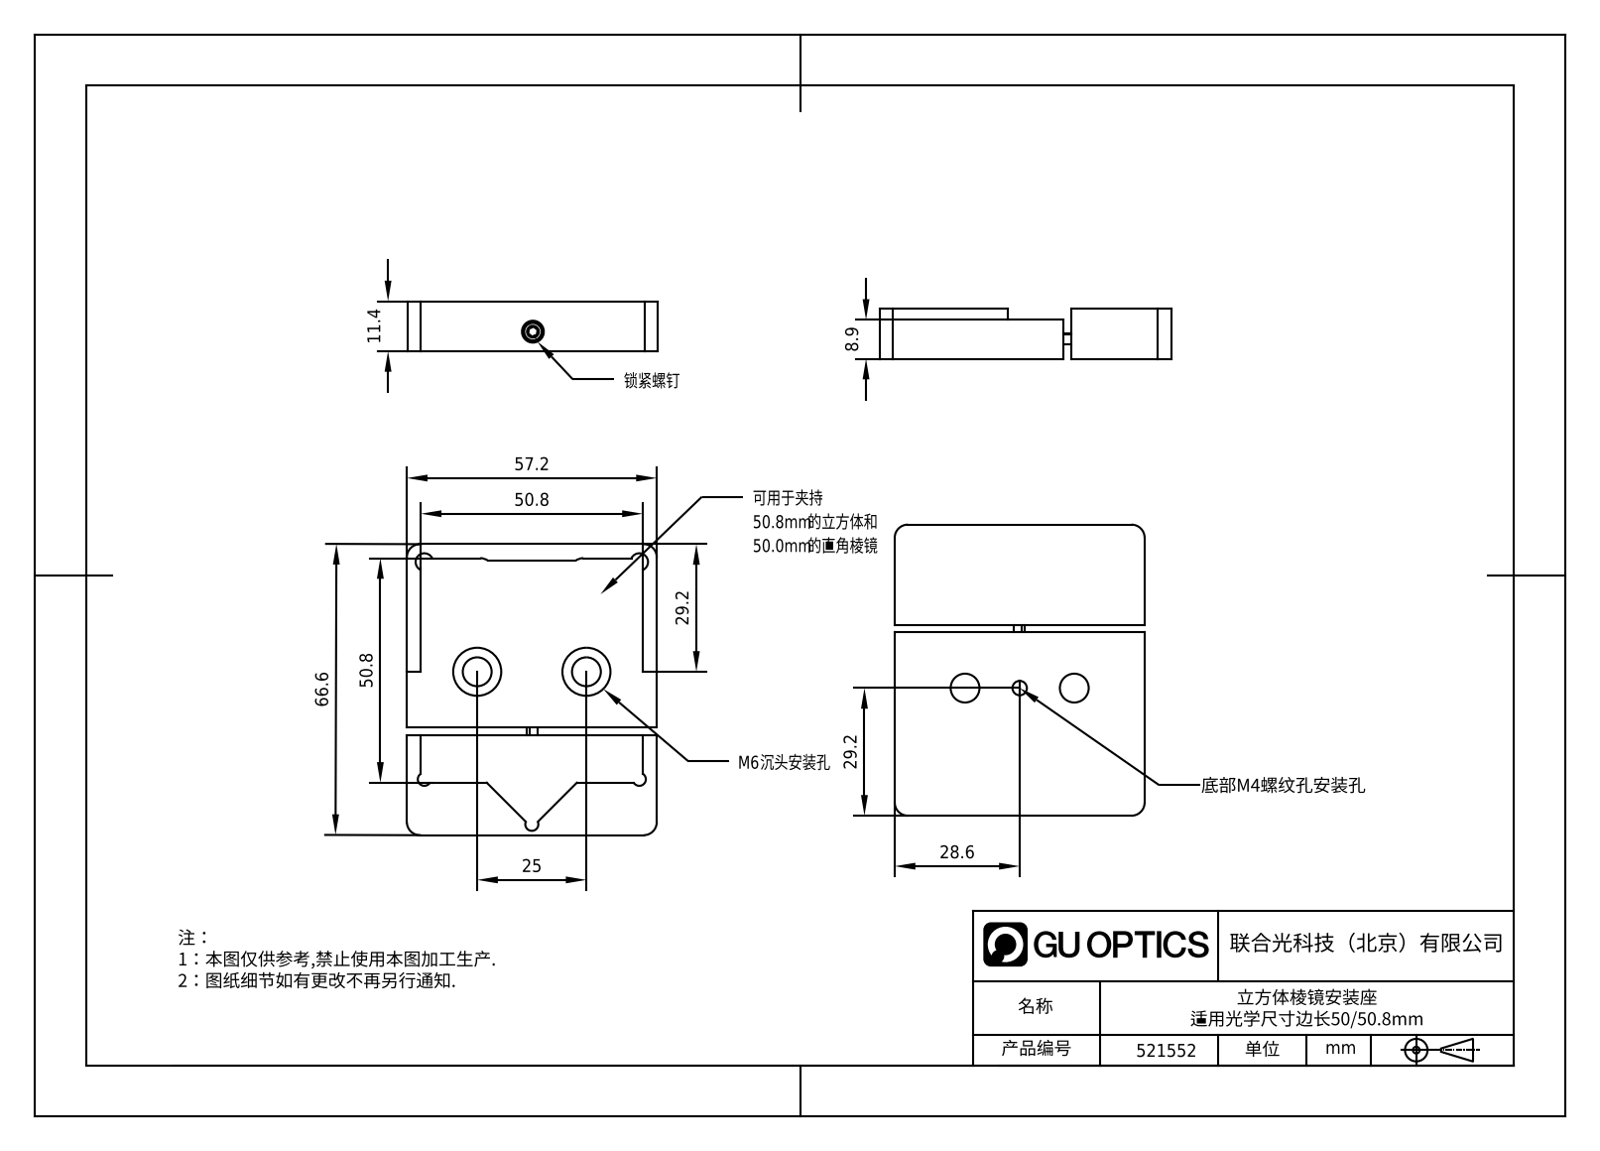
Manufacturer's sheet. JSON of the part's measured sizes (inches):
{"part_name": "1.3.13.3_ZZP-2.0_平台安装座，用于2英寸分束立方和直角棱镜，M4螺孔; 1.3.13.3.1_平台安装座主体1，用于2英寸分束立方和直角棱镜，M4螺孔; 1.3.13.3.2_平台安装座主体2，用于2英寸分束立方和直角棱镜，M4螺孔; 30.1.圆柱头内六角不锈钢螺丝_30.1.52-M2.5*25", "step_written_by": "SolidWorks 2021 (CONFIG_CONTROL_DESIGN)", "units": "inches", "bodies": {"solids": 3, "faces": 107, "planar": 48, "cylindrical": 47, "other": 12}, "overall_size": [2.622, 2.252, 0.449], "volume_in3": 2.054, "surface_area_in2": 20.03, "round_holes": [[0.118, 2], [0.157, 2], [0.26, 2], [0.433, 2], [0.081, 1], [0.114, 1], [0.13, 1], [0.197, 1]], "round_bosses_or_shafts": [[0.181, 1], [0.098, 1]], "partial_cylinders_radius": [[0.118, 6], [0.059, 3], [0.079, 2]], "face_to_face_distances": [0.35, 0.098, 0.449, 2.252, 2.622, 1.72, 0.902, 1.654, 0.067, 0.969], "hole_center_spacings": [0.492, 0.984, 1.476, 1.969]}
